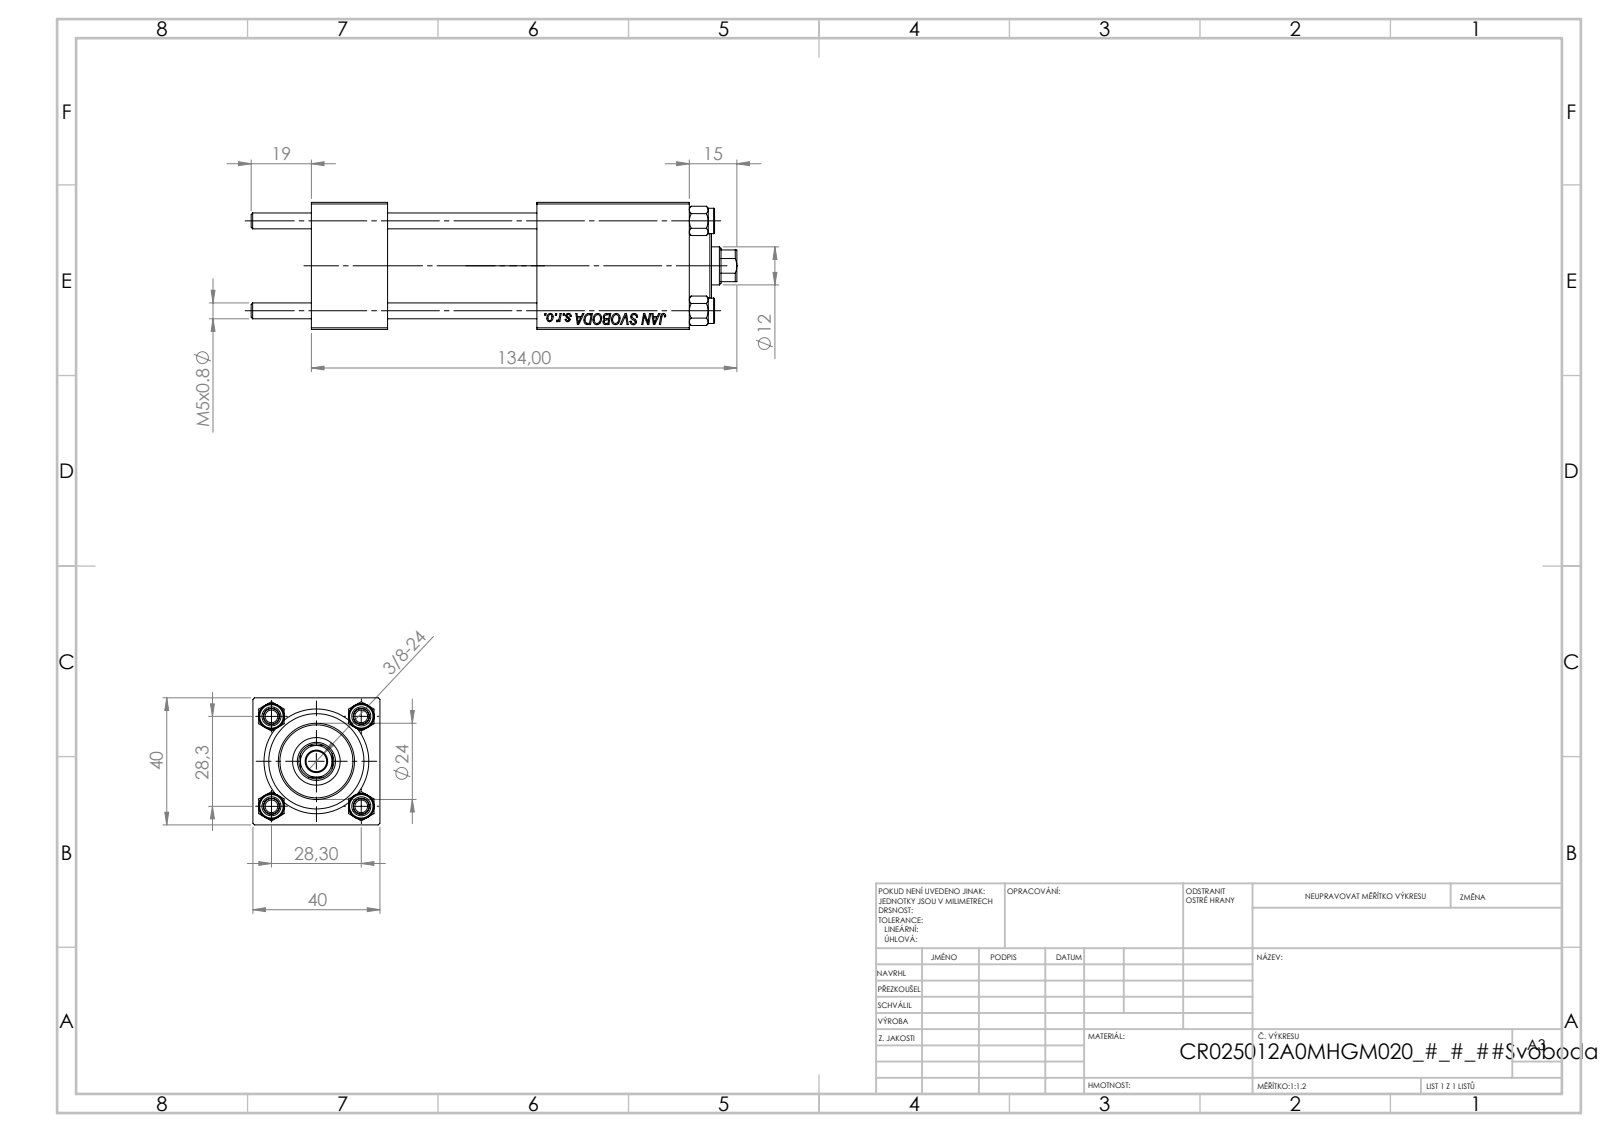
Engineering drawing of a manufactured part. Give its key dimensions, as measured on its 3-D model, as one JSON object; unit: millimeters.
{"part_name": "CR025_012_A_0_G_A_G_M_020_+#_##_TYCINKA; V215_VC_A; V215CR_BODY_A; V215CR_VCP (+1 more)", "step_written_by": "SolidWorks 2019 (CONFIG_CONTROL_DESIGN)", "units": "millimeters", "bodies": {"solids": 11, "faces": 1131, "planar": 517, "cylindrical": 78, "other": 536}, "overall_size": [153, 40, 40], "volume_mm3": 144824, "surface_area_mm2": 58872, "round_holes": [[5, 4], [20, 3], [7, 2], [13.16, 2], [6.5, 1], [12, 1], [15, 1], [25, 1], [30, 1]], "round_bosses_or_shafts": [[8, 4], [31, 1], [24, 1]], "partial_cylinders_radius": [[5.5, 1]], "face_to_face_distances": [40, 24, 119, 95, 90.3, 66.3, 28.7, 71, 47, 19.3], "hole_center_spacings": [20.01, 28.3, 40.02, 72]}
